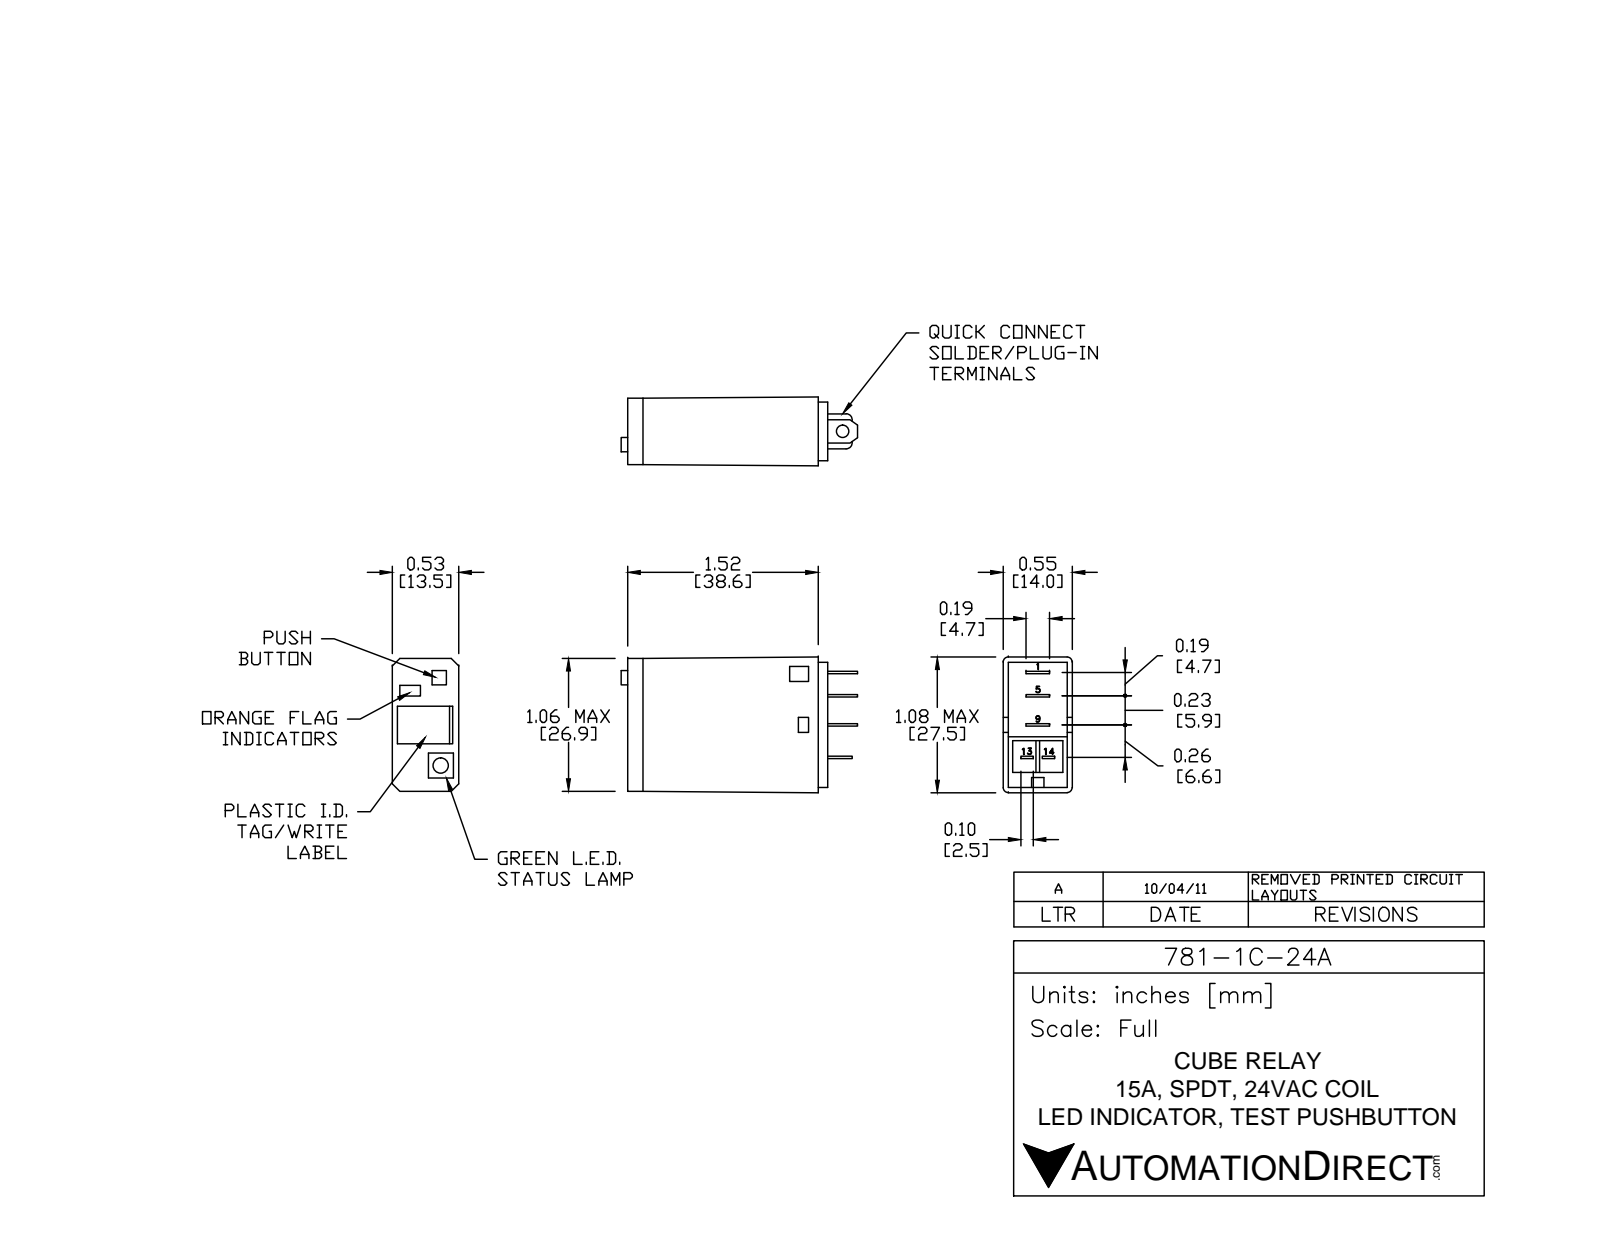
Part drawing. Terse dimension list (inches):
name: 781-1C-24A
written by: SolidWorks 2021 (CONFIG_CONTROL_DESIGN)
unit: in
bodies: 1 solid, 124 faces (109 planar, 15 cylindrical, 0 other)
size: 1.86 × 1.1 × 0.53
volume: 0.876 in³; area: 6.681 in²
holes: 2× ⌀0.07, 1× ⌀0.11, 1× ⌀0.125
rounds: 2× R0.062, 1× R0.155
face distances: 1.6, 0.02, 0.08, 0.185, 1.52, 0.19, 0.2, 0.195, 0.45, 1.515
hole spacings: 0.08, 0.16
